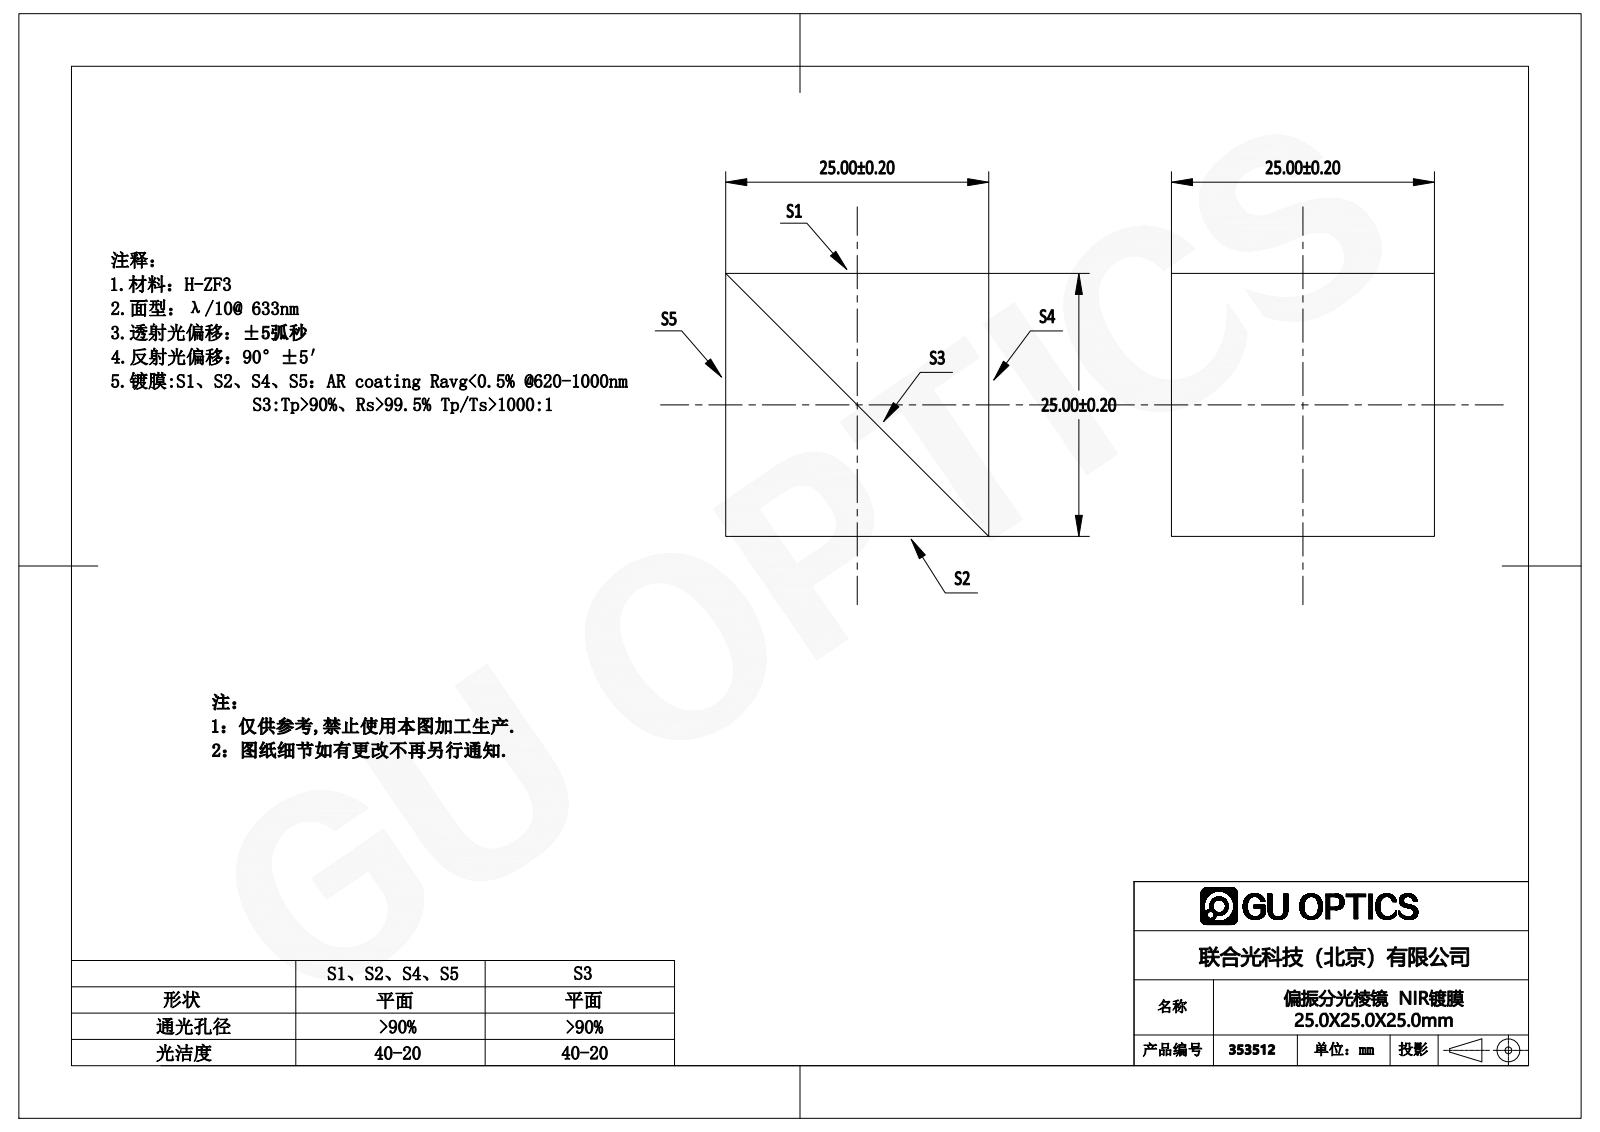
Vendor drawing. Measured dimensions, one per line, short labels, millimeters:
name: 352515
written by: SolidWorks 2016 (AUTOMOTIVE_DESIGN)
unit: mm
bodies: 2 solids, 10 faces (10 planar, 0 cylindrical, 0 other)
size: 25 × 25 × 25
volume: 15 625 mm³; area: 5 518 mm²
face distances: 25
